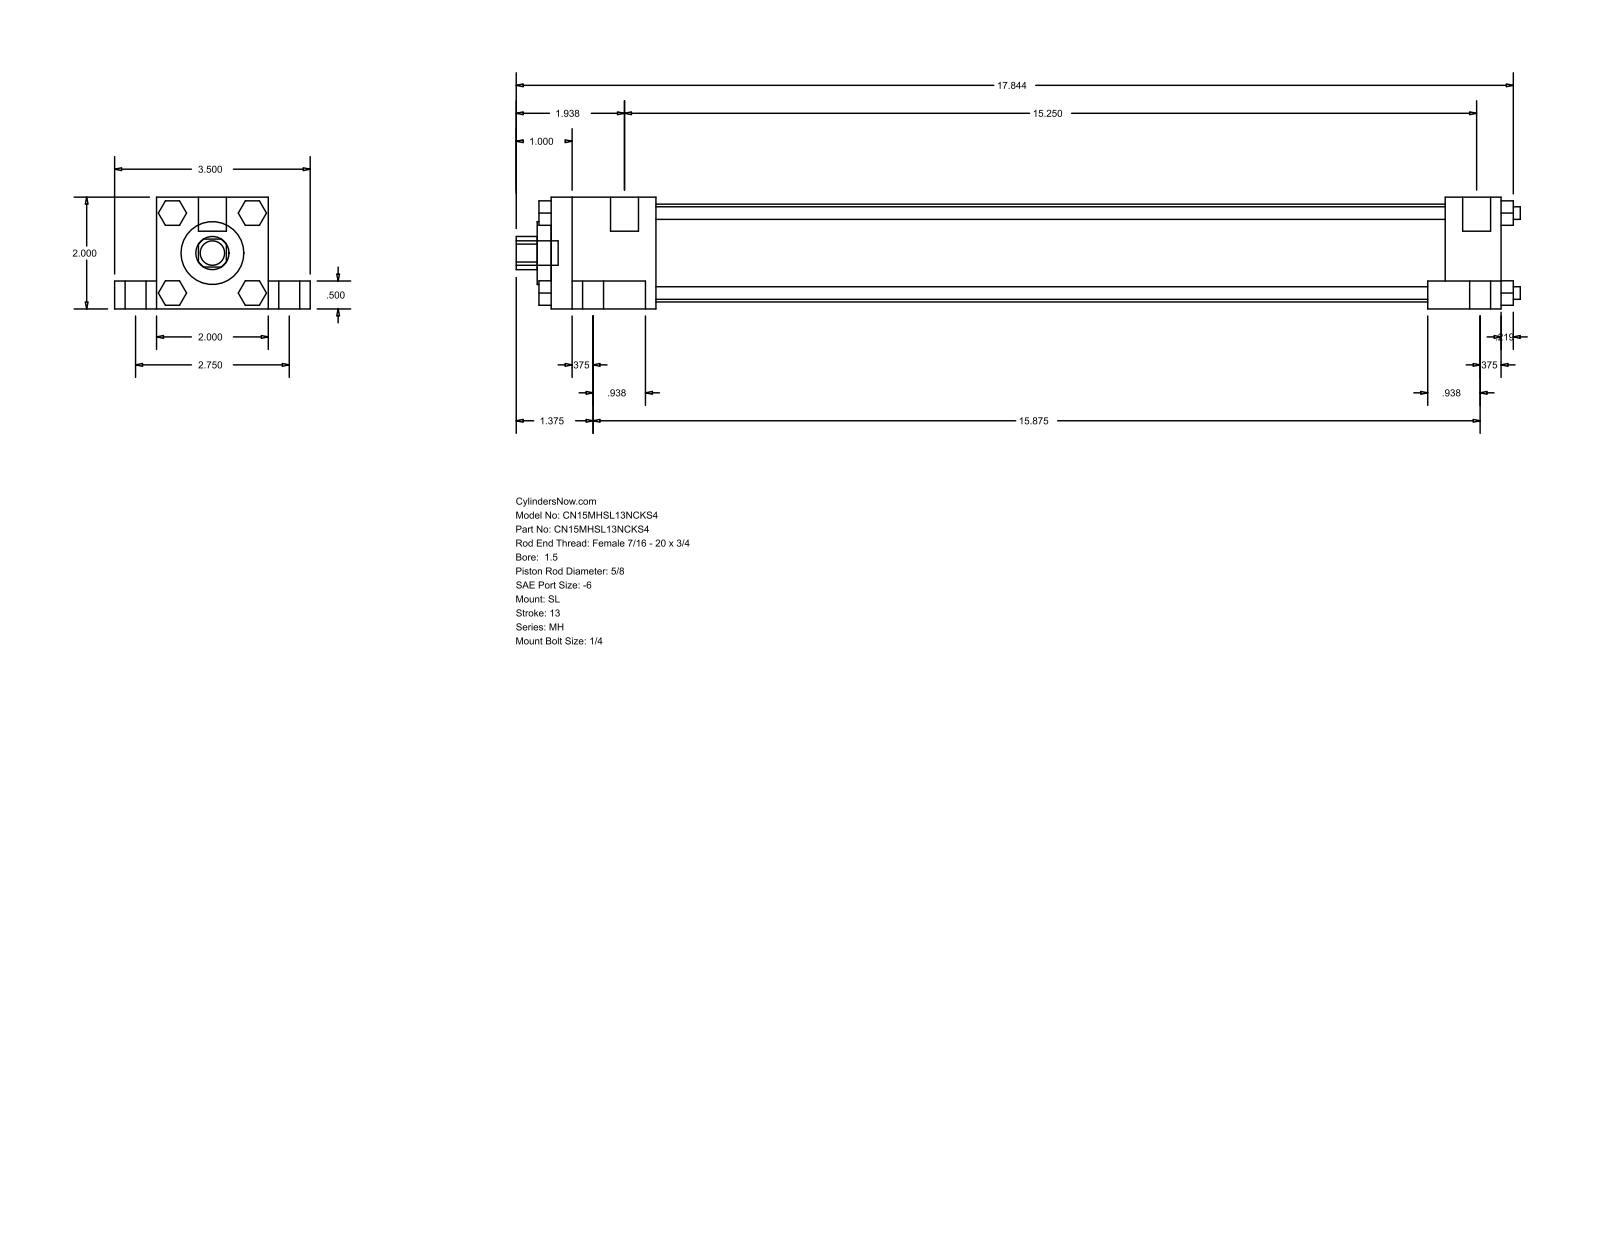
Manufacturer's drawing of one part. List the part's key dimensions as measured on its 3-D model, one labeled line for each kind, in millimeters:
Part name (STEP PRODUCT): MH_SL__0150_0.625
STEP written by: GSSL Pune (CONFIG_CONTROL_DESIGN)
Units: millimetres
Bodies: 0 solids, 148 faces (112 planar, 36 cylindrical, 0 other)
Overall size (bounding box): 456.41 × 88.9 × 50.8
Round holes (diameter × count): ⌀15.88 ×1, ⌀28.57 ×1, ⌀44.45 ×1
Round bosses / shafts (diameter × count): ⌀15.88 ×4, ⌀9.53 ×4, ⌀5.71 ×4, ⌀5.56 ×4, ⌀12.7 ×2, ⌀11.11 ×1
Partial cylindrical surfaces — rounded edges, fillets, slot ends (radius × count): R7.54 ×1
Main face-to-face distances: 50.8, 38.1, 19.05, 12.7, 69.85, 431.8, 9.52, 33.34, 388.94, 406.39
